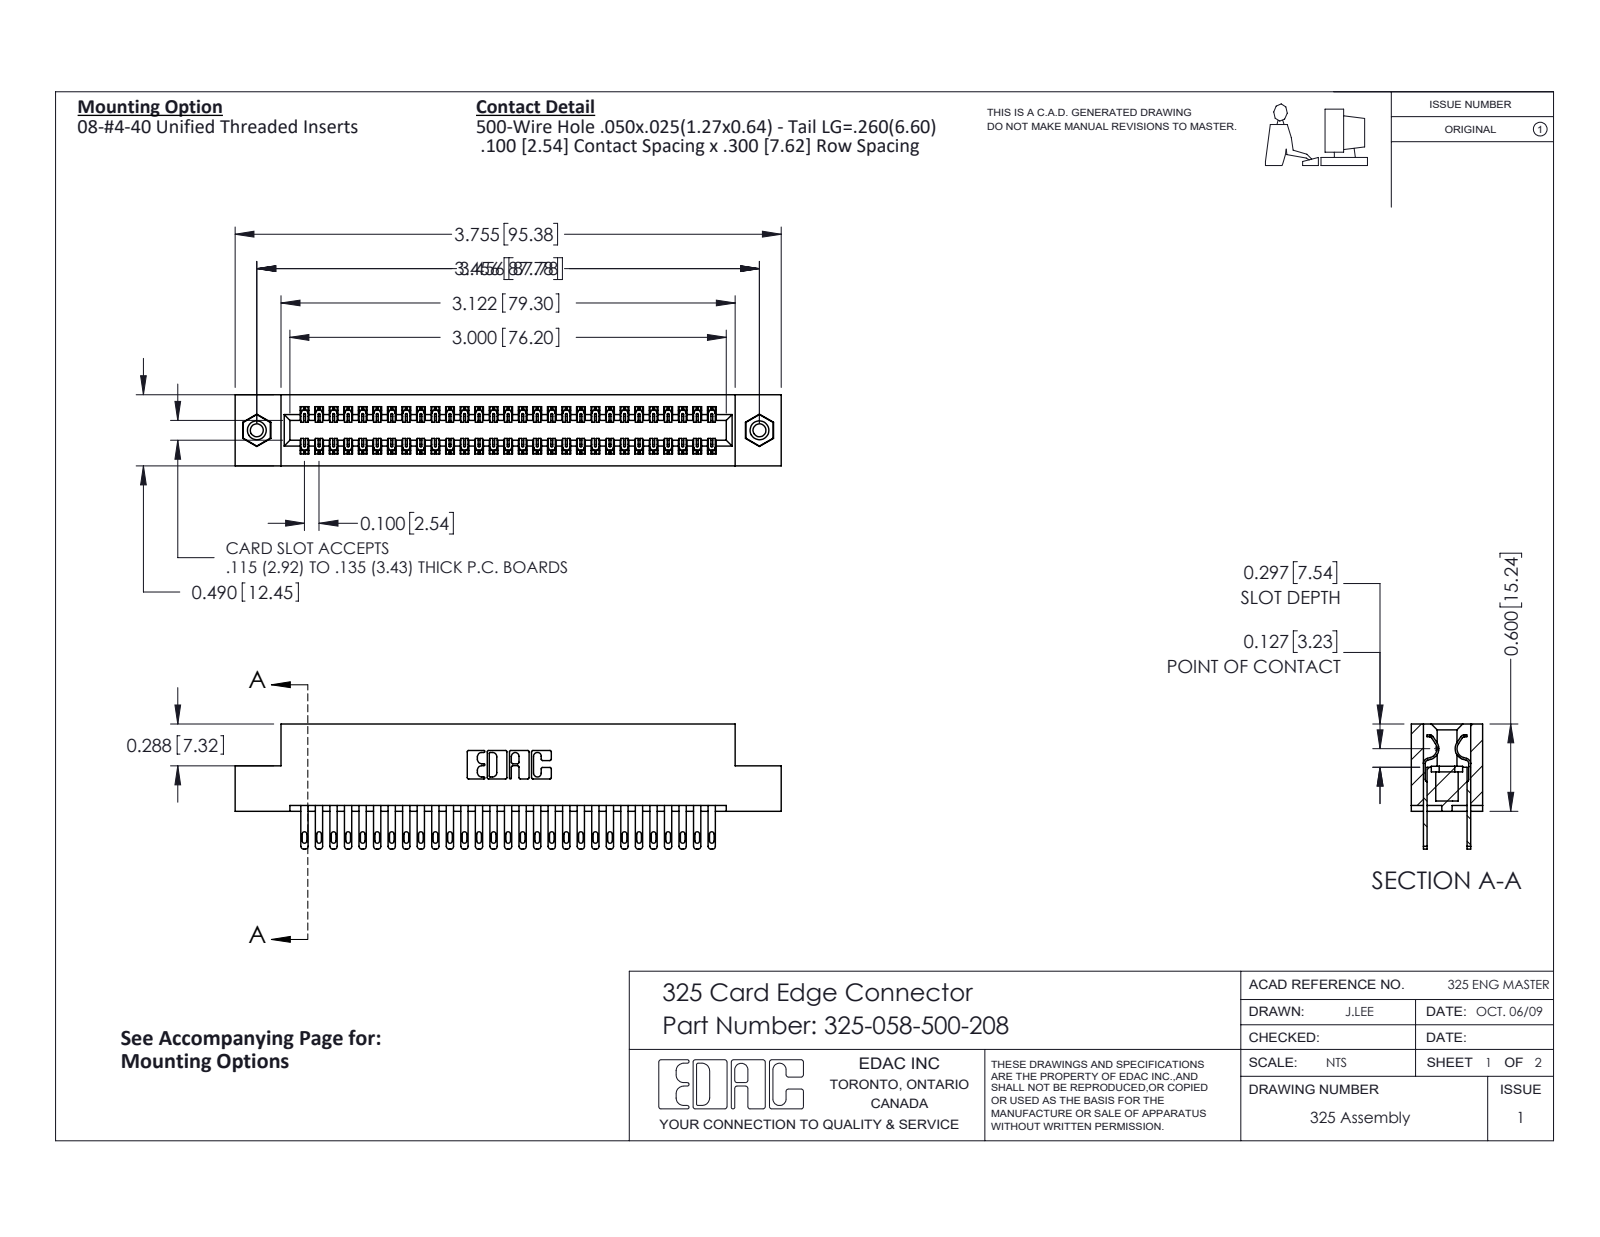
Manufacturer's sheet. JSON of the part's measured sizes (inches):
{"part_name": "325-058-500-208; 325-292-001_325-293-100; 345-250-001_345-250-003-102; 325 Part_TI", "step_written_by": "SolidWorks 2016 (CONFIG_CONTROL_DESIGN)", "units": "inches", "bodies": {"solids": 61, "faces": 2958, "planar": 1842, "cylindrical": 1100, "other": 16}, "overall_size": [3.755, 0.86, 0.49], "volume_in3": 0.755, "surface_area_in2": 23.68, "round_holes": [[0.089, 2], [0.125, 2], [0.16, 2]], "round_bosses_or_shafts": [[0.155, 2]], "partial_cylinders_radius": [[0.006, 87], [0.016, 58], [0.02, 58], [0.01, 22], [0.007, 6], [0.031, 6], [0.026, 3], [0.014, 2]], "face_to_face_distances": [0.083, 0.407, 0.3, 0.107, 0.383, 0.025, 0.49, 0.325, 0.275, 0.04], "hole_center_spacings": [3.456]}
